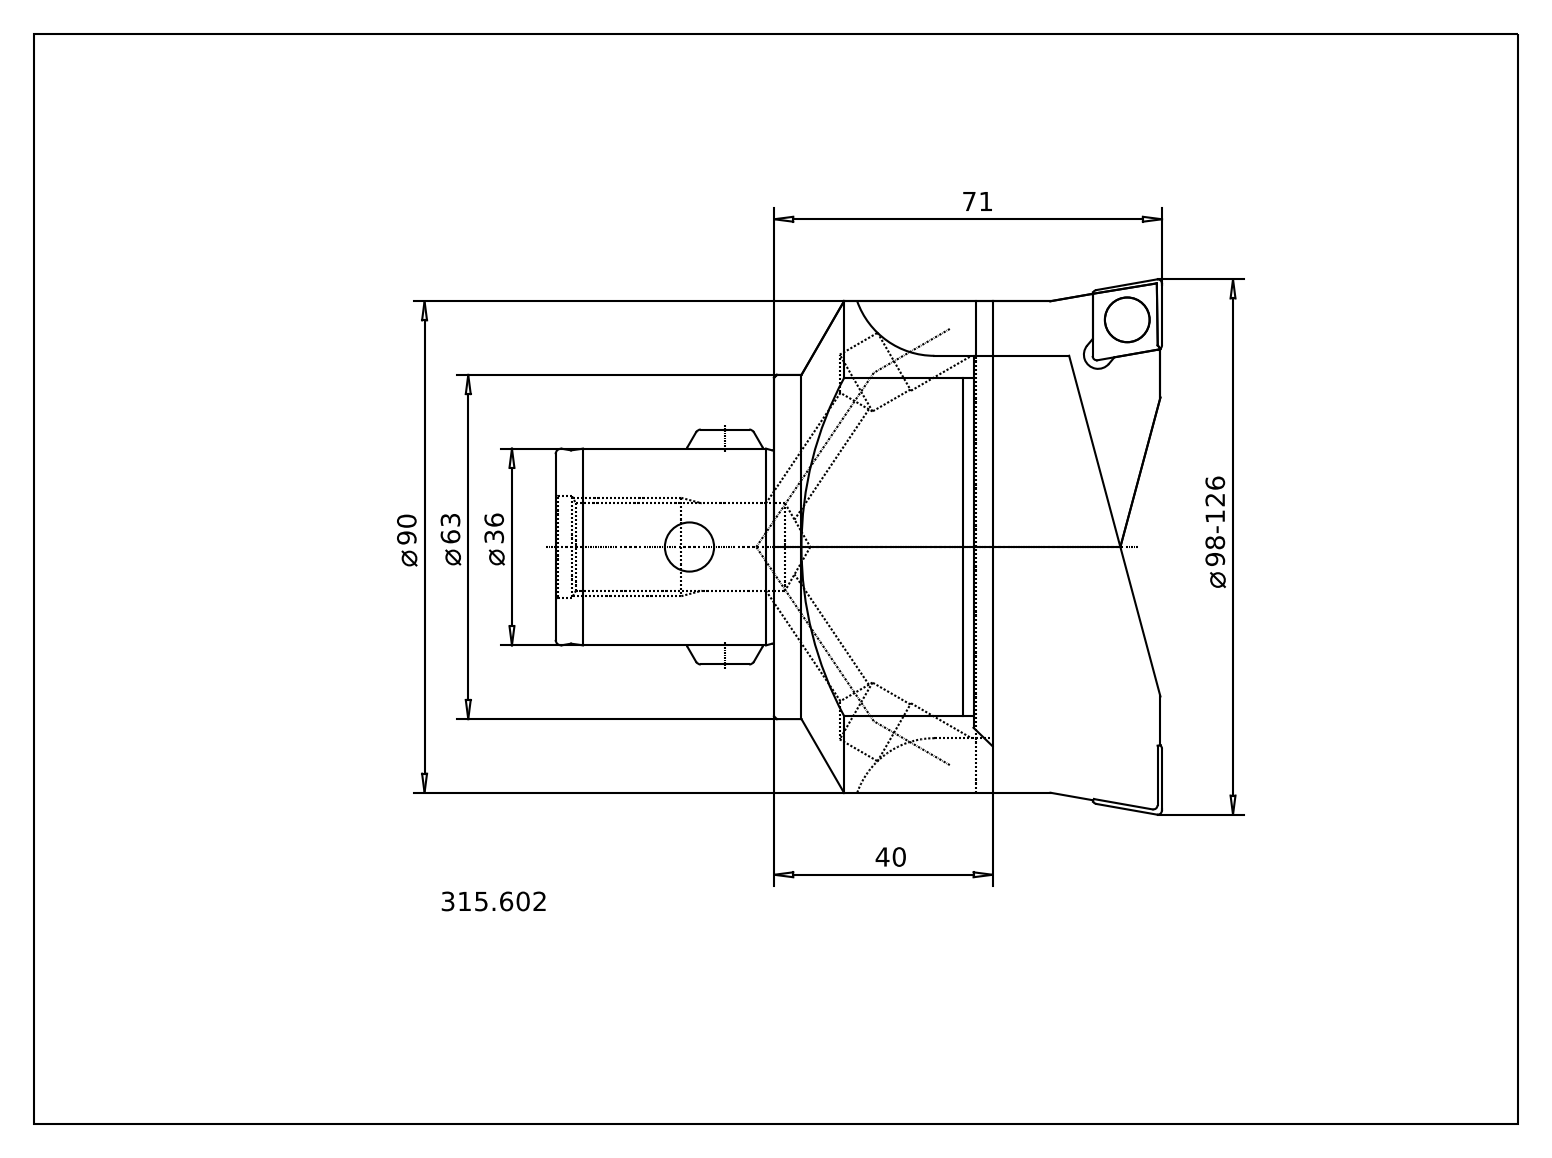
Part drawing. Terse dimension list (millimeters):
name: 315.602 Kaiser TWN 98-153 X CK6|315.750 Kaiser ETL M12_12.15 X 44_Standard;NONE; 315.602 Kaiser TWN 98-153 X CK6|691.506 Kaiser ETL �14 X 43K_Standard|691.526 Mitnehmerbolzen_Standard;NONE; 315.602 Kaiser TWN 98-153 X CK6|691.506 Kaiser ETL �14 X 43K_Standard|693.305 Skizze_Standard;NONE; 315.602 Kaiser TWN 98-153 X CK6|315.632 Kaiser TW 98-153 X CK6B_Standard|315.632 Kaiser TW 98-153 X CK6B_Standard;NONE
written by: ACIS (automotive_design)
unit: mm
bodies: 15 solids, 457 faces (89 planar, 132 cylindrical, 236 other)
size: 115 × 90 × 65
volume: 223 777 mm³; area: 54 259 mm²
holes: 6× ⌀12, 4× ⌀10, 4× ⌀10.2, 4× ⌀12.5, 2× ⌀4.3, 2× ⌀6, 2× ⌀7.8, 2× ⌀12.2, 1× ⌀9, 1× ⌀14, 1× ⌀16, 1× ⌀18.5
bosses: 4× ⌀20, 4× ⌀12.15, 4× ⌀11.65, 4× ⌀9.4, 2× ⌀11.7, 1× ⌀63, 1× ⌀36, 1× ⌀13.93
rounds: 2× R1, 1× R45
face distances: 40, 65, 3, 37, 25.5, 22, 32.5, 25, 70, 35
hole spacings: 16.12, 21.26, 24, 29.12, 32.25, 42.52
